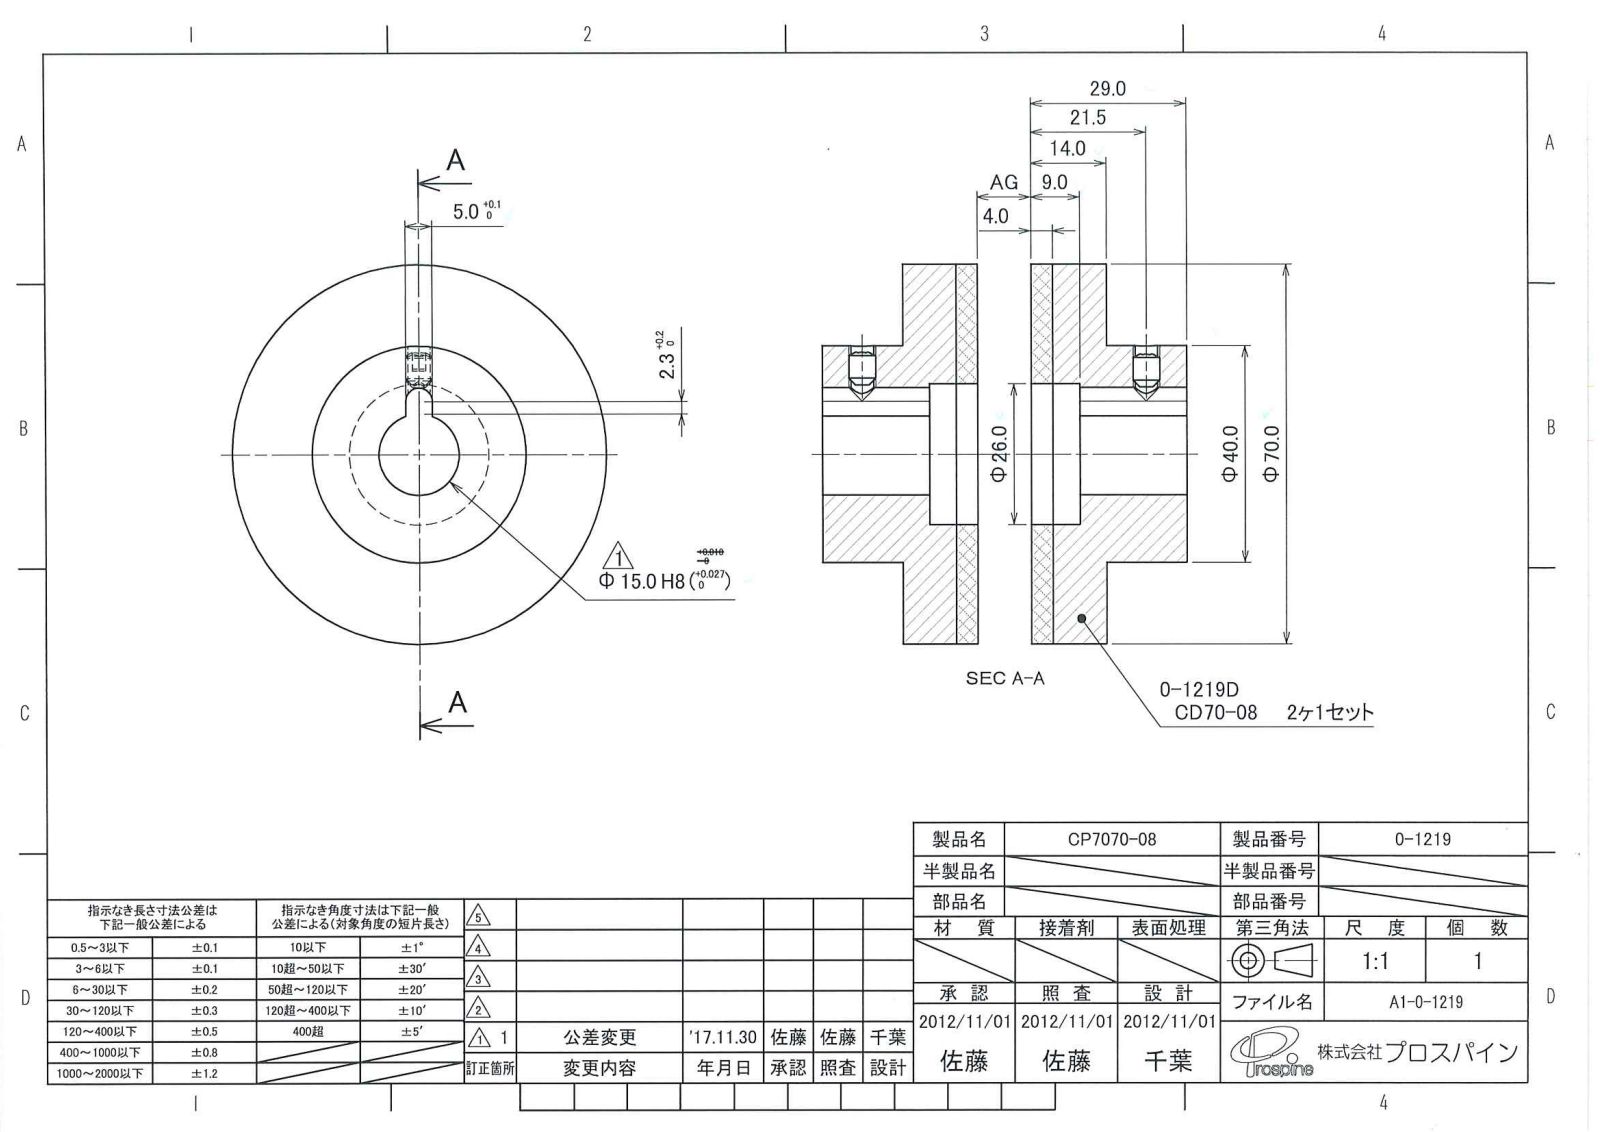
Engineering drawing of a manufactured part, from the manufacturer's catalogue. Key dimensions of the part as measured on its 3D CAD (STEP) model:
STEP written by: PSStep 10.0 (CONFIG_CONTROL_DESIGN)
Units: millimetres
Bodies: 4 solids, 38 faces (22 planar, 10 cylindrical, 6 other)
Overall size (bounding box): 70 × 70 × 29
Volume: 64 035 mm³ · Surface area: 21 095 mm²
Round holes (diameter × count): ⌀4.2 ×1, ⌀15 ×1, ⌀26 ×1
Round bosses / shafts (diameter × count): ⌀70 ×1, ⌀40 ×1, ⌀5 ×1
Partial cylindrical surfaces — rounded edges, fillets, slot ends (radius × count): R2.5 ×1
Main face-to-face distances: 4, 10, 14, 15, 25, 29, 5, 20, 9, 2.5
